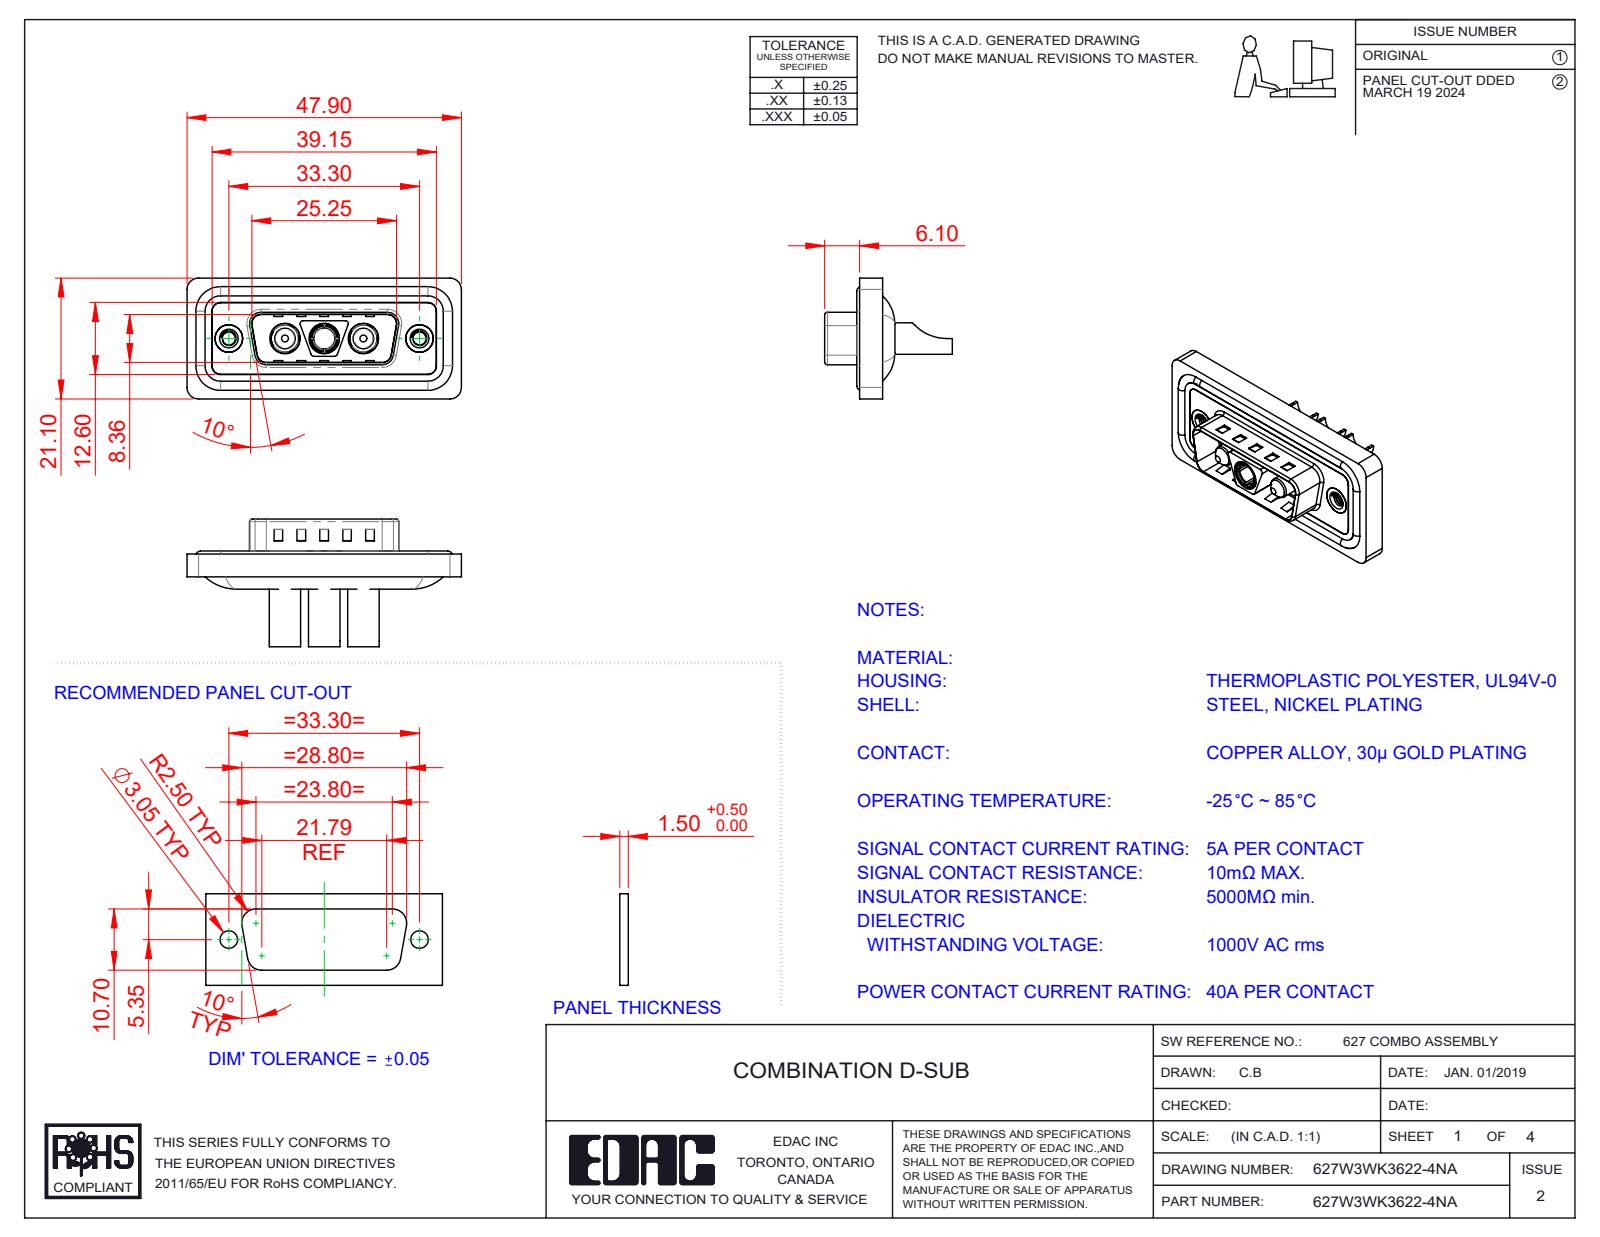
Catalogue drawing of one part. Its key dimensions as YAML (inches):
part_name: "627Combo Shell Front_15 Contacts; Power Pin_40A SC; 627Combo Threaded Rivet_A; 627W3WK3622-4NA (+4 more)"
step_written_by: "SolidWorks 2023 (CONFIG_CONTROL_DESIGN)"
units: inches
bodies: {solids: 13, faces: 619, planar: 237, cylindrical: 255, other: 127}
overall_size: [1.886, 0.878, 0.831]
volume: 0.354
surface_area: 14.79
round_holes:
  - {diameter: 0.181, count: 3}
  - {diameter: 0.191, count: 3}
  - {diameter: 0.209, count: 3}
  - {diameter: 0.089, count: 2}
  - {diameter: 0.157, count: 2}
  - {diameter: 0.189, count: 2}
  - {diameter: 0.197, count: 2}
  - {diameter: 0.146, count: 1}
round_bosses_or_shafts:
  - {diameter: 0.063, count: 4}
  - {diameter: 0.217, count: 3}
  - {diameter: 0.205, count: 3}
  - {diameter: 0.187, count: 3}
  - {diameter: 0.148, count: 3}
  - {diameter: 0.193, count: 2}
  - {diameter: 0.142, count: 2}
  - {diameter: 0.195, count: 1}
partial_cylinders:
  - {radius: 0.059, count: 26}
  - {radius: 0.079, count: 20}
  - {radius: 0.02, count: 12}
  - {radius: 0.063, count: 8}
  - {radius: 0.01, count: 4}
  - {radius: 0.024, count: 4}
  - {radius: 0.026, count: 4}
  - {radius: 0.035, count: 4}
face_to_face_distances: [0.016, 0.043, 0.02, 0.063, 0.122, 0.114, 0.059, 0.032, 0.377, 0.098]
hole_center_spacings: [0.27, 0.386, 0.656, 0.925, 0.539, 1.311]
